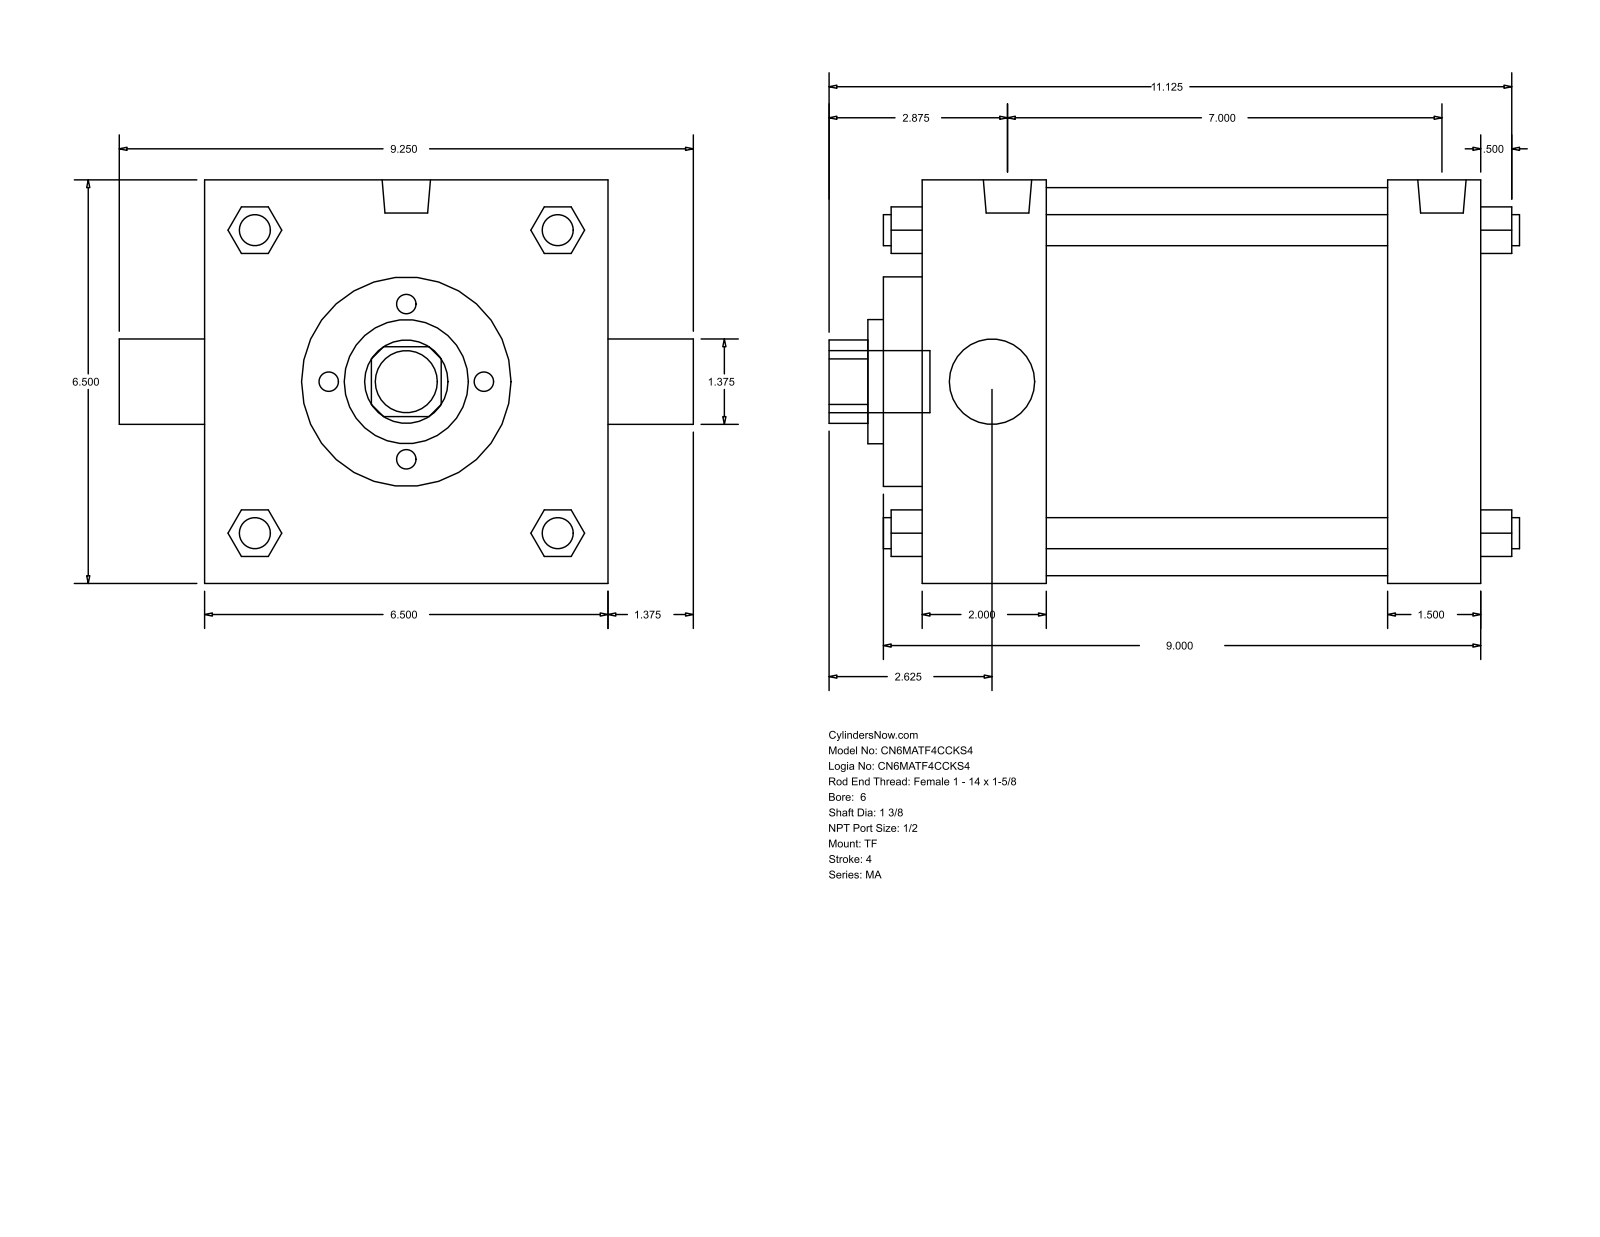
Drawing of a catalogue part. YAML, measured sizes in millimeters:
part_name: "MA_TF__0600_1.375"
step_written_by: "GSSL Pune (CONFIG_CONTROL_DESIGN)"
units: millimeters
bodies: {solids: 0, faces: 122, planar: 93, cylindrical: 29, other: 0}
overall_size: [282.57, 234.95, 165.1]
round_holes:
  - {diameter: 34.92, count: 2}
  - {diameter: 50.8, count: 1}
  - {diameter: 85.72, count: 1}
  - {diameter: 158.75, count: 1}
round_bosses_or_shafts:
  - {diameter: 12.7, count: 4}
  - {diameter: 17.46, count: 3}
  - {diameter: 19.77, count: 2}
  - {diameter: 25.4, count: 1}
partial_cylinders:
  - {radius: 17.06, count: 1}
face_to_face_distances: [165.1, 231.78, 38.1, 50.8, 180.98, 193.68, 142.88, 15.87, 66.67, 209.55]
